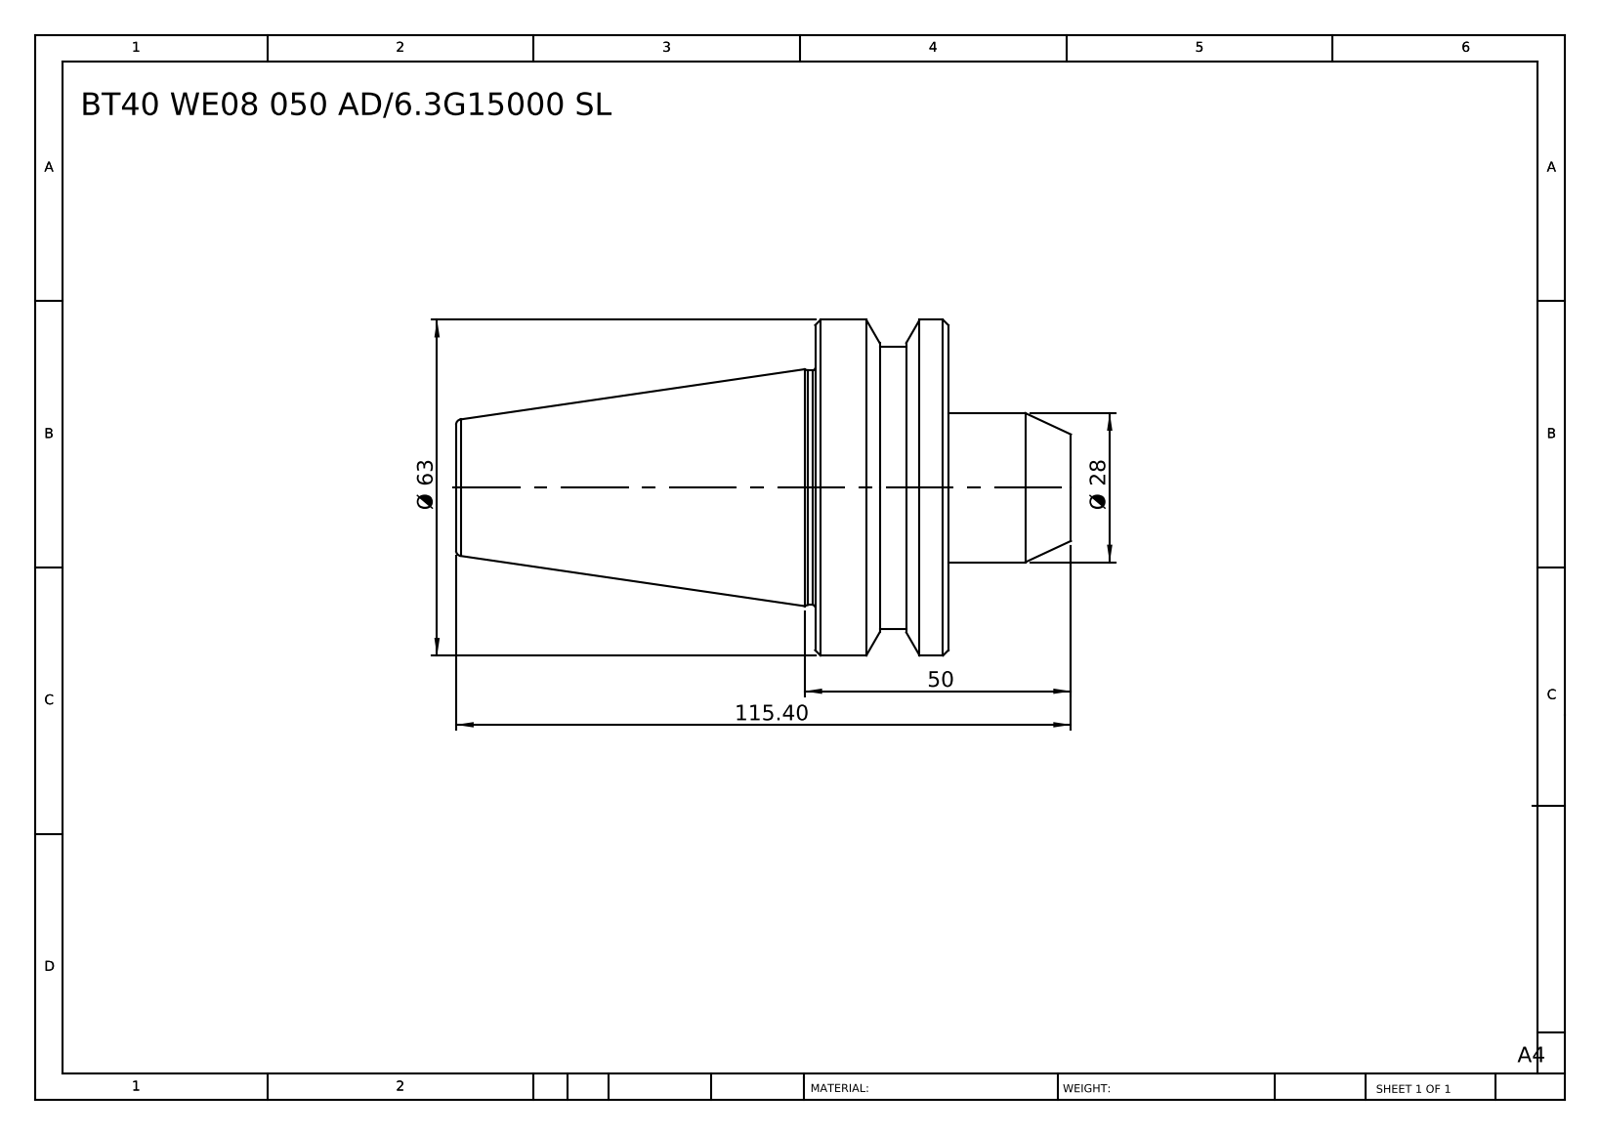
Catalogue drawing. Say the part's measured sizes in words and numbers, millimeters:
The part is named "BT40 WE08 050 AD-6.3G15000 SL". Its 3-D file was written by "SolidWorks 2014 (CONFIG_CONTROL_DESIGN)". It is 1 solid with 36 faces: 6 planar, 10 cylindrical and 20 other. Overall it measures 115.4 by 63 by 63 millimeters. Its volume is 151 144 cubic millimeters and its surface area 20 013 square millimeters. Round bosses or shafts: 1 of diameter 63, 1 of diameter 53, 1 of diameter 44, 1 of diameter 28. The main face-to-face distances are 25, 92.4, 67.4, 23, 48, 115.4, 35.9, 12.9, 12.1, 79.5.
